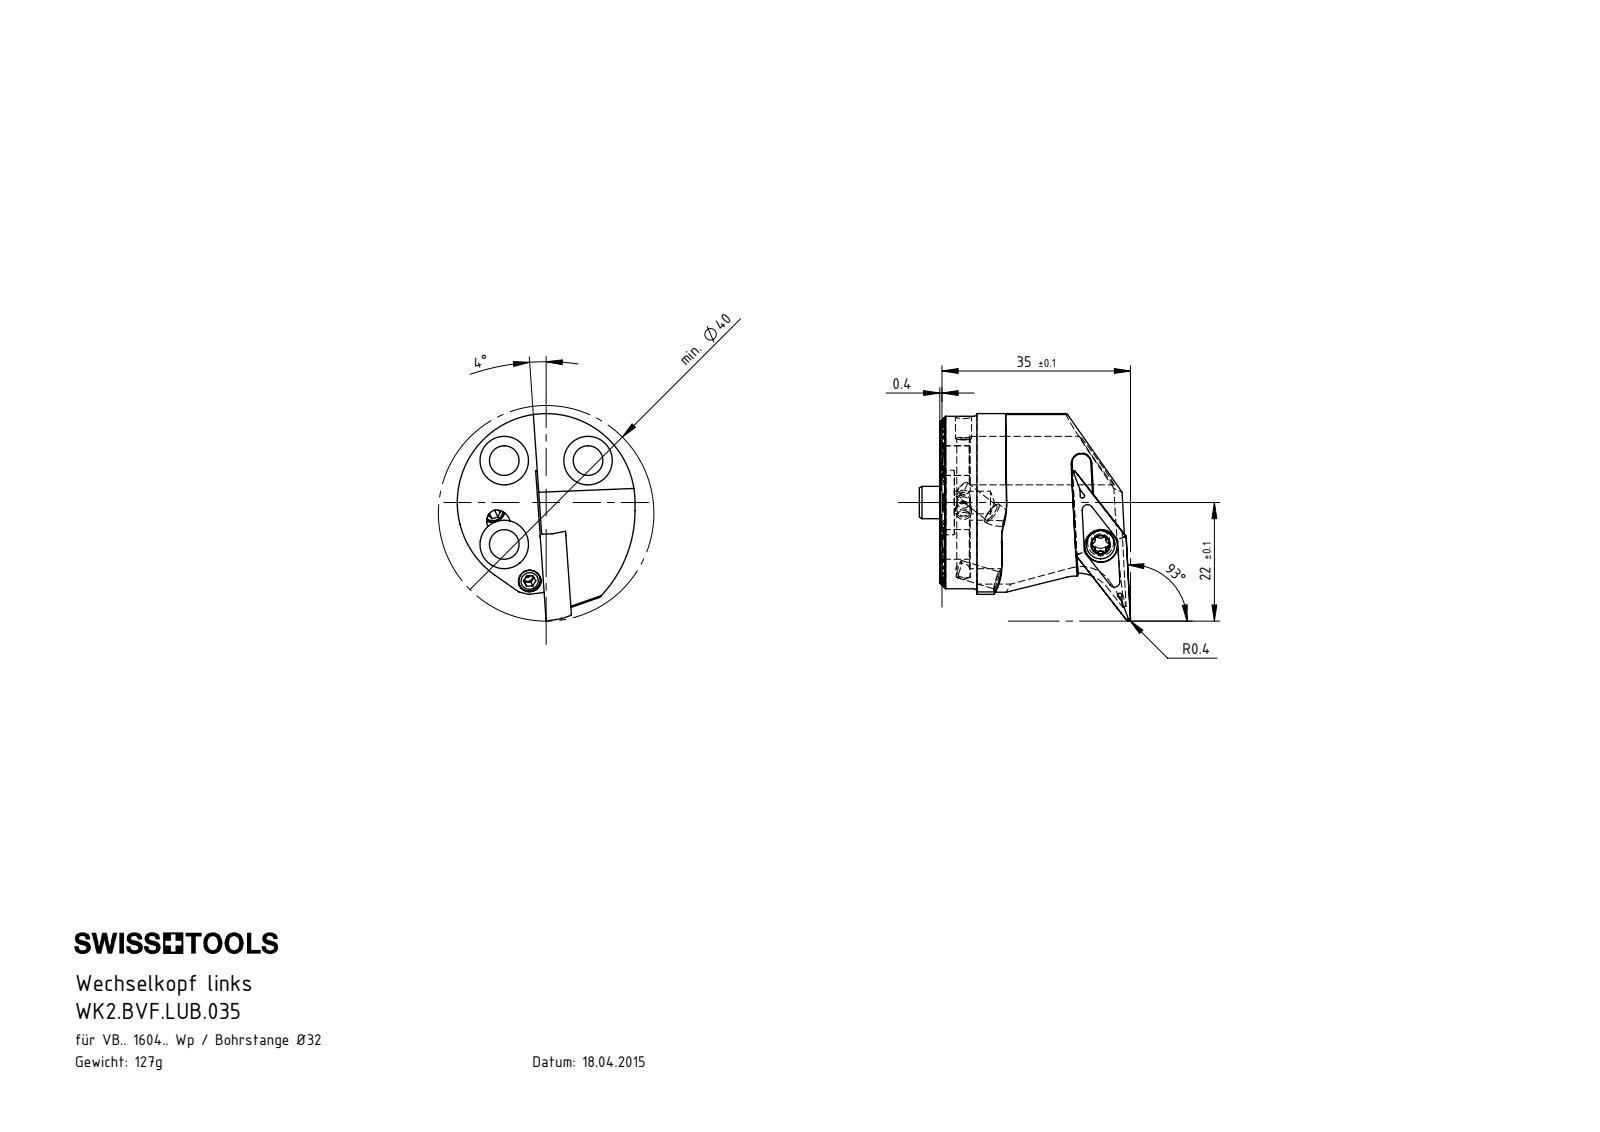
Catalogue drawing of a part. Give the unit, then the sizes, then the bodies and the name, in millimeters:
Units: millimetres
Overall size (bounding box): 39.2 × 38.5 × 33
Round holes (diameter × count): ⌀3.3 ×3, ⌀4.2 ×3, ⌀5.5 ×3, ⌀9 ×3, ⌀1.7 ×2, ⌀2.38 ×2, ⌀2.5 ×2, ⌀3 ×2, ⌀4.4 ×1, ⌀6.1 ×1, ⌀12 ×1
Round bosses / shafts (diameter × count): ⌀4 ×3, ⌀3 ×2, ⌀32 ×1, ⌀6 ×1, ⌀5.25 ×1
Partial cylindrical surfaces — rounded edges, fillets, slot ends (radius × count): R0.12 ×22, R0.34 ×6, R0.59 ×6, R12 ×3, R0.15 ×2, R1.75 ×1, R7 ×1, R16.5 ×1
Main face-to-face distances: 1.3, 2.6, 3.9, 5.2, 6.5, 12.99, 11.69, 4.46, 14.29, 7.8
Hole centre spacings: 11, 15.56, 22.01
Volume: 15 748 mm³ · Surface area: 8 534 mm²
Bodies: 10 solids, 532 faces (198 planar, 186 cylindrical, 148 other)
Part name (STEP PRODUCT): VBMT160404; KVT_MB_600_030; WK2-BVF.LUB.035_A; WK2.BVF.LUB.035 (+3 more)
STEP written by: SolidWorks 2017 (AUTOMOTIVE_DESIGN)
